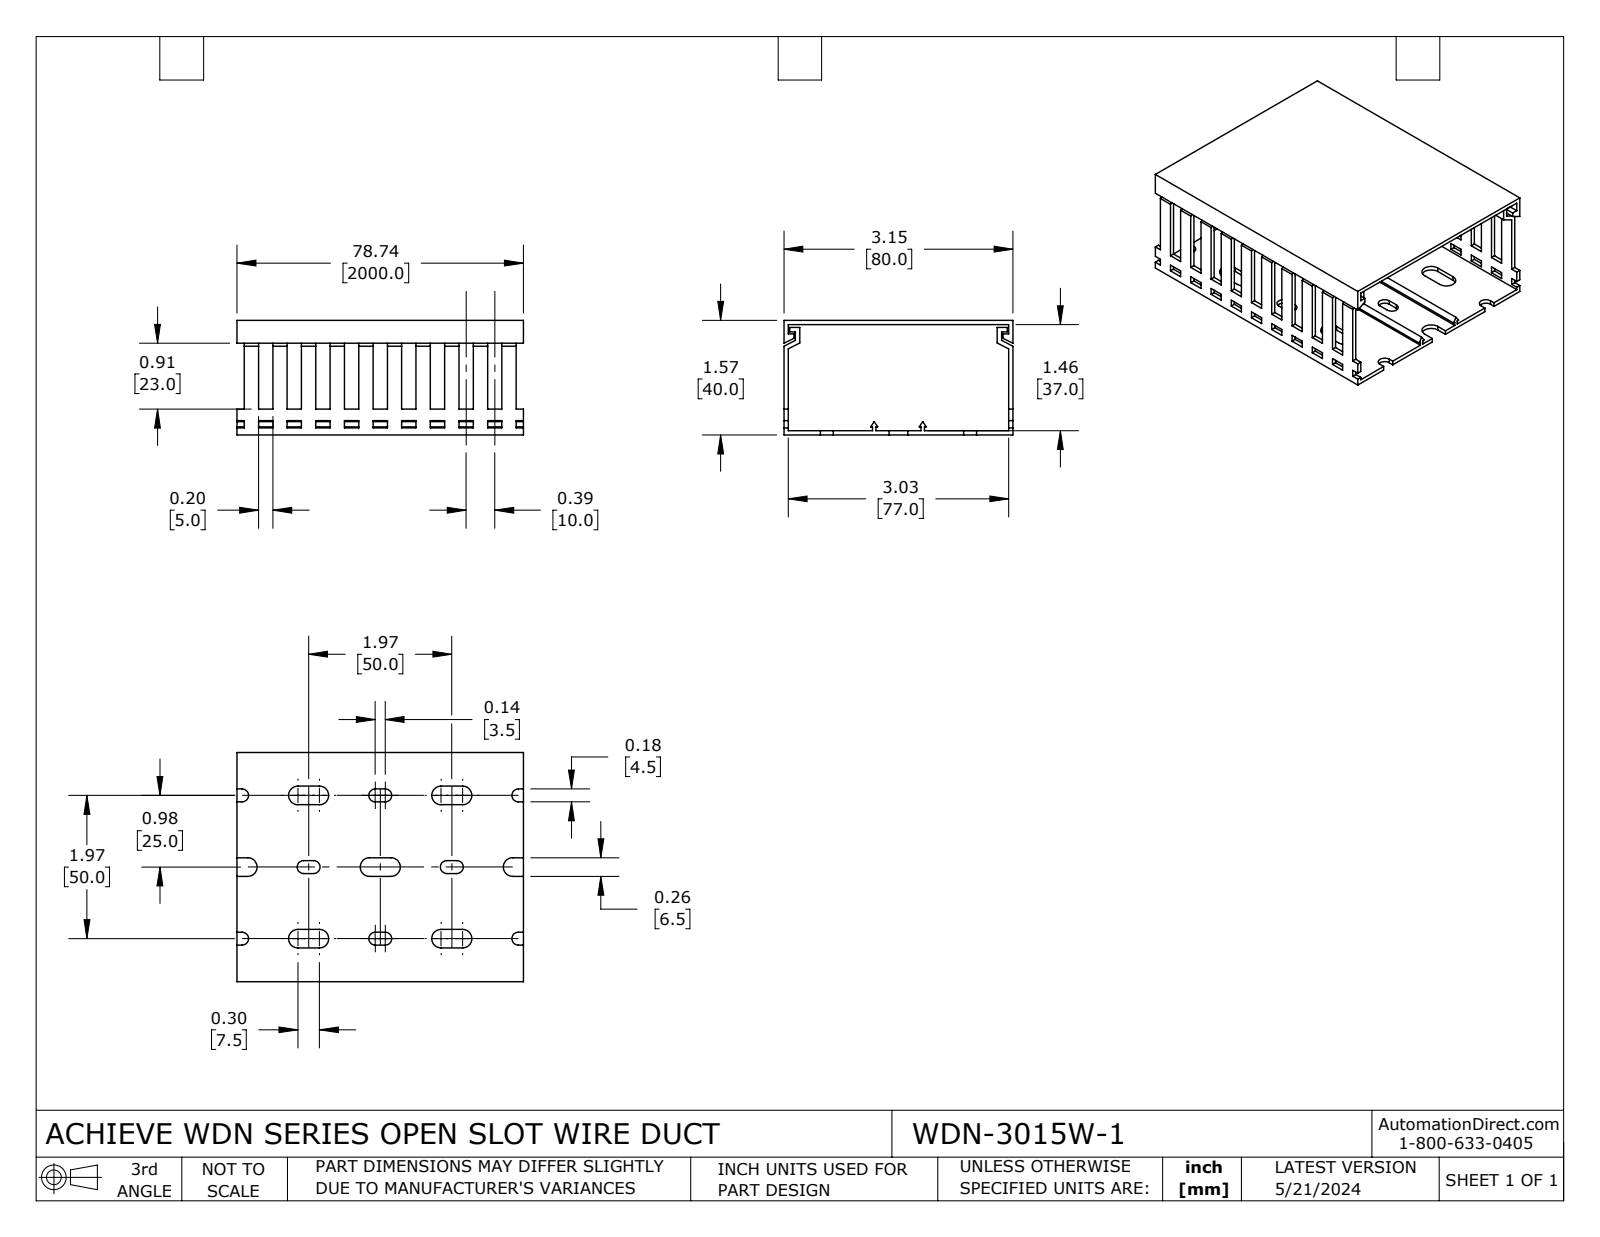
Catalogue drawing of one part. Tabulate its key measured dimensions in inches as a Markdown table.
| quantity | value |
| --- | --- |
| part name | WDN-3015W-1 |
| STEP written by | SolidWorks 2023 (CONFIG_CONTROL_DESIGN) |
| units | inches |
| bodies | 2 solids, 398 faces (362 planar, 36 cylindrical, 0 other) |
| overall size | 3.937 × 3.15 × 1.575 |
| volume | 2.026 in³ |
| surface area | 74.96 in² |
| partial cylindrical surfaces (radius × count) | 0.089 × 12, 0.128 × 12 |
| main face-to-face distances | 0.059, 1.516, 1.575, 1.457, 3.091, 3.15, 3.031, 0.197, 0.394, 0.591 |
